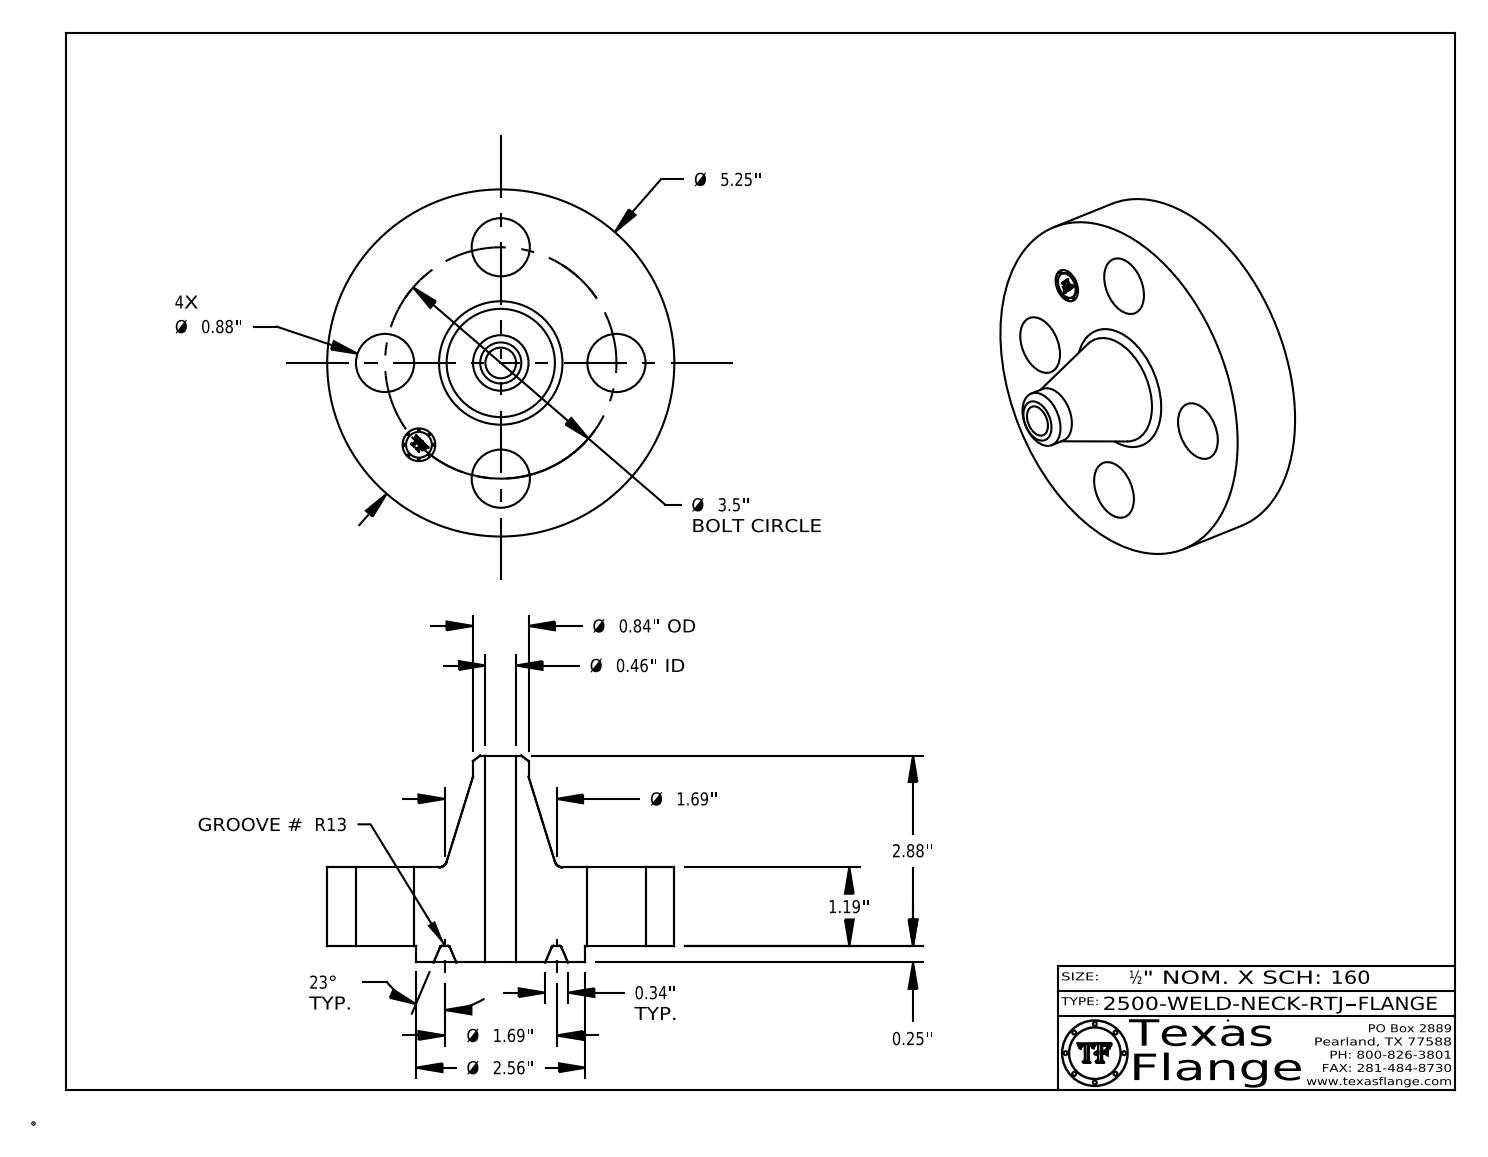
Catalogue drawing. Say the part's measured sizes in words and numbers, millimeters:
The part is named "2500-WELD-NECK-RTJ". Its 3-D file was written by "CATIA V5 STEP AP214 (AUTOMOTIVE_DESIGN)". It is 1 solid with 421 faces: 371 planar, 36 cylindrical and 14 other. Overall it measures 133.4 by 133.4 by 79.5 millimeters. Its volume is 414 100 cubic millimeters and its surface area 54 080 square millimeters. Round holes: 4 of diameter 22.4, 1 of diameter 11.8, 1 of diameter 12.6. Round bosses or shafts: 8 of diameter 0.8, 1 of diameter 133.4, 1 of diameter 65.1, 1 of diameter 21.3, 1 of diameter 9.9. The main face-to-face distances are 30.2, 6.4, 36.6, 79.5, 73.2, 42.9, 36.2, 29.8, 0.4, 43.3. The hole center spacings are 44.5, 62.9, 34, 82.1, 88.9.
